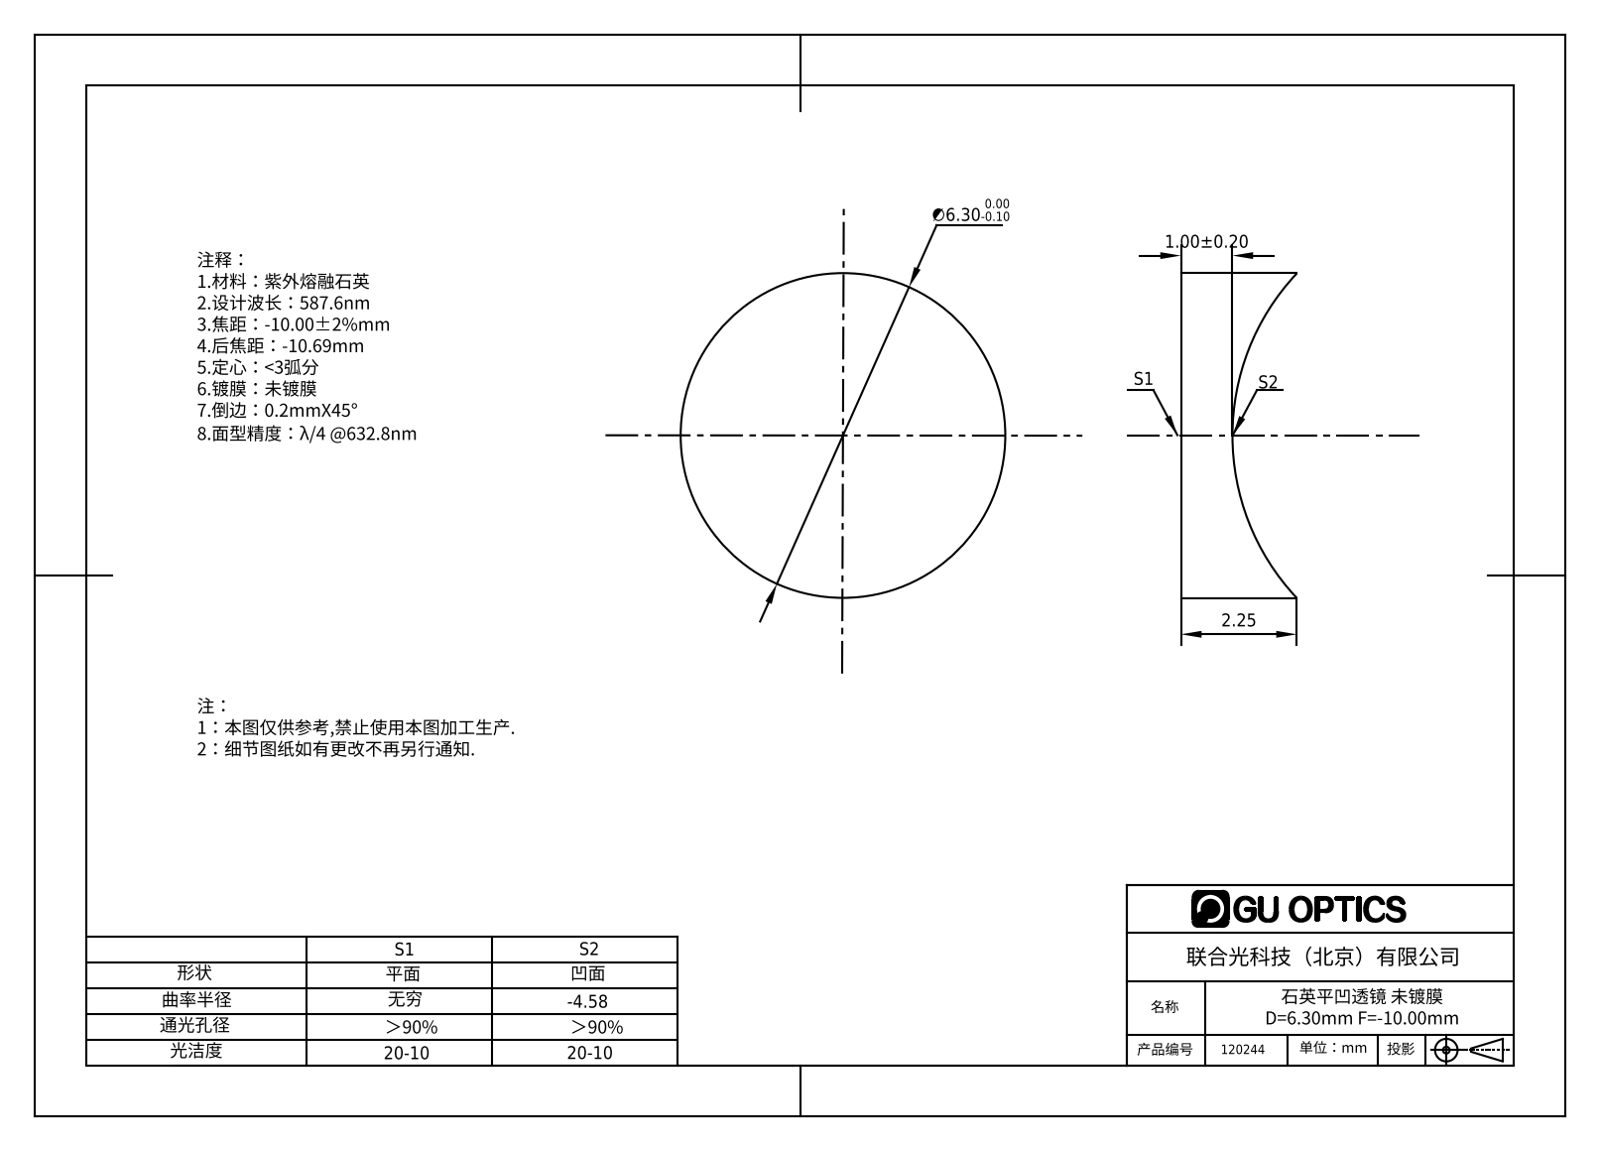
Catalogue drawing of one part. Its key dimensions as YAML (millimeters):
part_name: "120244"
step_written_by: "SolidWorks 2016 (AUTOMOTIVE_DESIGN)"
units: millimeters
bodies: {solids: 1, faces: 5, planar: 1, cylindrical: 2, other: 2}
overall_size: [6.3, 6.3, 2.25]
volume: 50
surface_area: 112
round_bosses_or_shafts:
  - {diameter: 6.3, count: 1}
